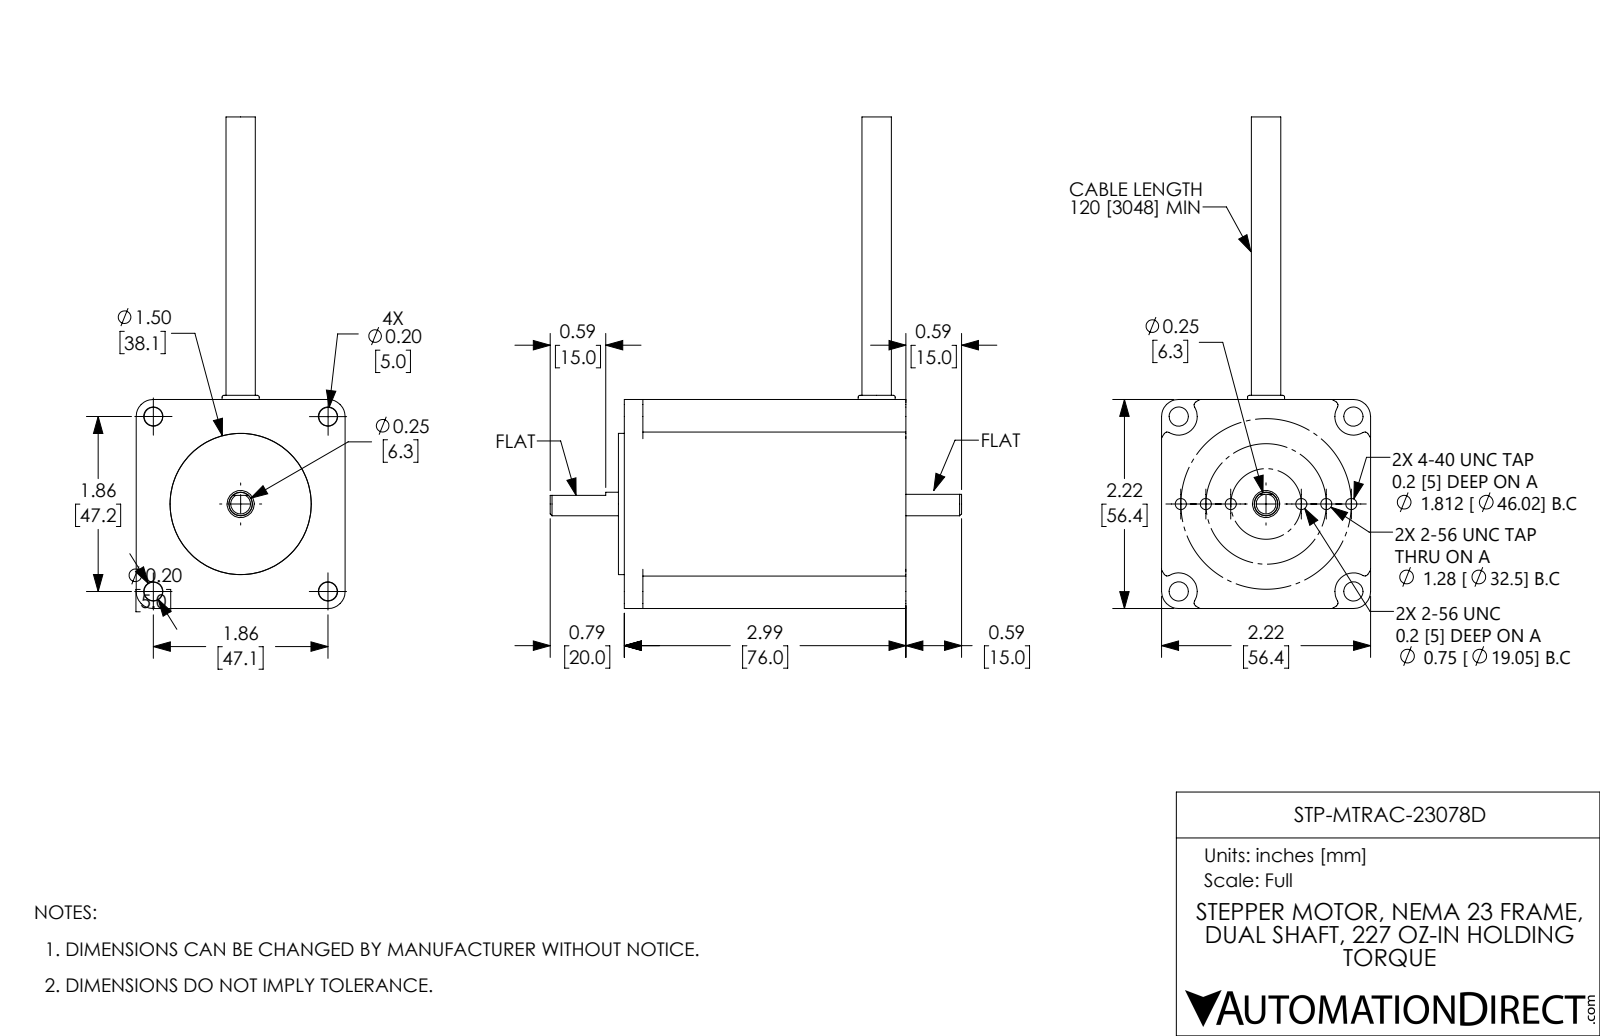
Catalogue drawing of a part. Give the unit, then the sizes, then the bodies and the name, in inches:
Units: inches
Overall size (bounding box): 5.22 × 4.37 × 2.22
Round holes (diameter × count): ⌀0.118 ×6
Round bosses / shafts (diameter × count): ⌀0.312 ×1
Main face-to-face distances: 2.22, 2.992, 3.055, 0.063, 0.197, 2.795, 0.26, 1.202, 1.019, 1.214
Hole centre spacings: 0.265, 0.266, 0.531, 1.015, 1.281, 1.546, 0.75, 1.28
Volume: 13.65 in³ · Surface area: 40.61 in²
Bodies: 1 solid, 139 faces (27 planar, 14 cylindrical, 98 other)
Part name (STEP PRODUCT): STP-MTRAC-23078D from HT23-554-CAA New r1b
STEP written by: SolidWorks 2017 (AUTOMOTIVE_DESIGN)
